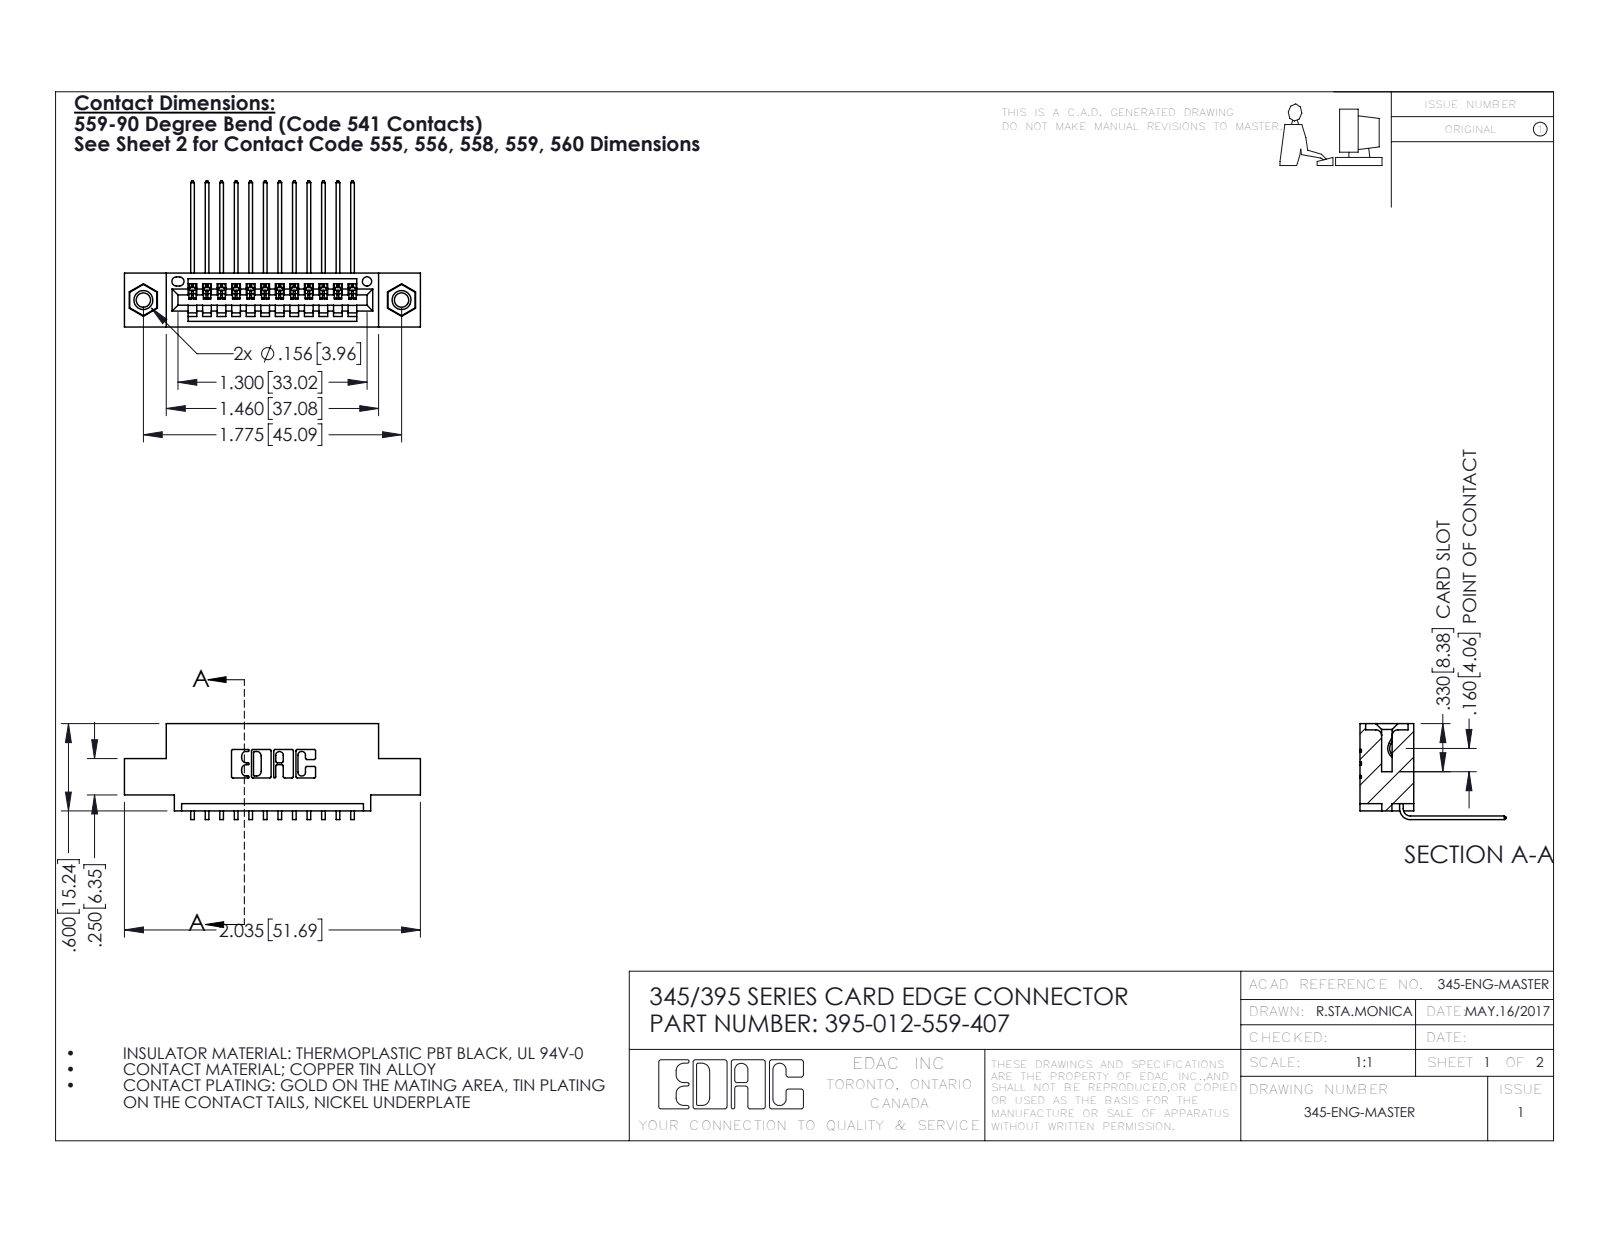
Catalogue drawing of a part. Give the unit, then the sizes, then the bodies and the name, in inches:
Units: inches
Overall size (bounding box): 2.035 × 1.005 × 0.659
Round holes (diameter × count): ⌀0.098 ×2, ⌀0.125 ×2, ⌀0.156 ×2, ⌀0.064 ×1
Round bosses / shafts (diameter × count): ⌀0.155 ×2
Partial cylindrical surfaces — rounded edges, fillets, slot ends (radius × count): R0.006 ×24, R0.01 ×22, R0.007 ×6, R0.031 ×6, R0.026 ×3, R0.031 ×2, R0.04 ×2, R0.014 ×1
Main face-to-face distances: 0.2, 0.072, 0.298, 0.37, 0.098, 0.272, 0.025, 0.1, 0.16, 0.3
Hole centre spacings: 0.27, 1.543, 1.775
Volume: 0.282 in³ · Surface area: 9.419 in²
Bodies: 15 solids, 910 faces (620 planar, 274 cylindrical, 16 other)
Part name (STEP PRODUCT): 345 Part_0.110 Offset - 0.156 Dia-TI; 345-292-001_558 559 Tail - 1; 395-012-559-407; 345-250-001_345-250-005-103
STEP written by: SolidWorks 2016 (CONFIG_CONTROL_DESIGN)
